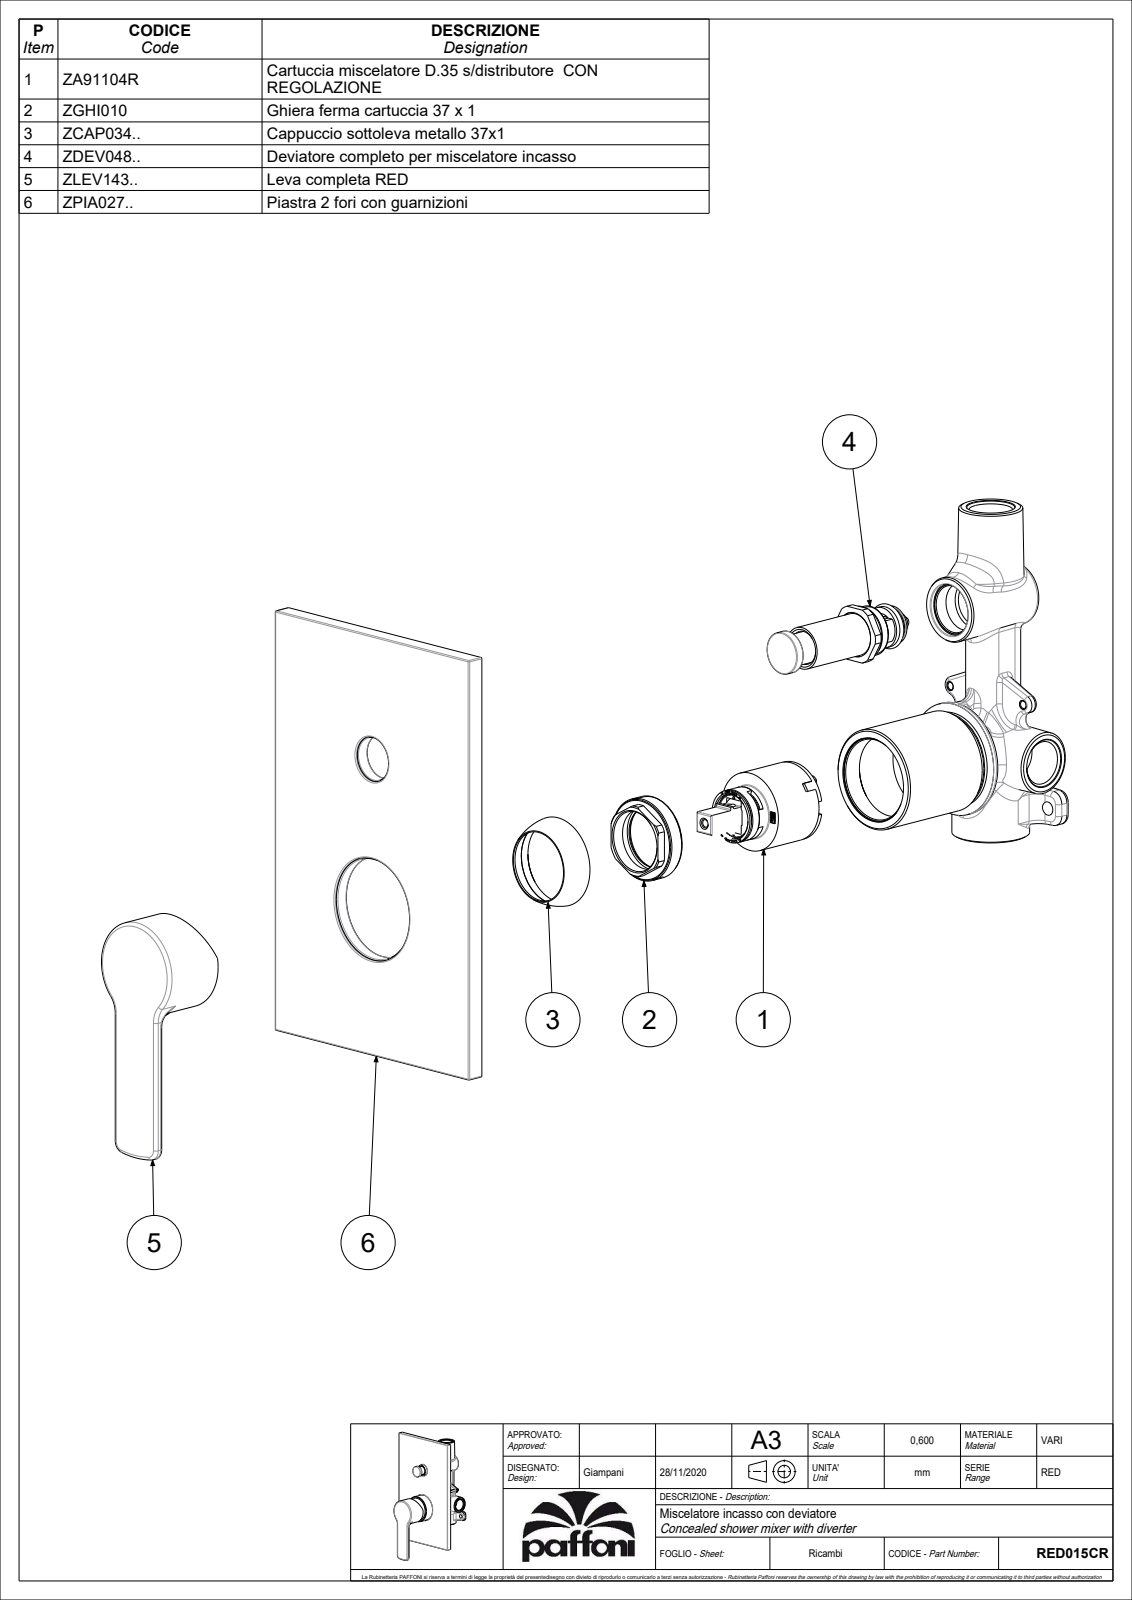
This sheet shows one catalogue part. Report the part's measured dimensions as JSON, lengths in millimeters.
{"part_name": "RED015CR", "step_written_by": "CREO PARAMETRIC BY PTC INC, 2020044 (CONFIG_CONTROL_DESIGN)", "units": "millimeters", "bodies": {"solids": 5, "faces": 1152, "planar": 617, "cylindrical": 301, "other": 234}, "overall_size": [209, 120, 64.83], "volume_mm3": 171443, "surface_area_mm2": 98513, "round_holes": [[3.3, 2], [4, 2], [3, 1], [4.5, 1], [5, 1], [10.5, 1], [14.8, 1], [19.2, 1], [19.5, 1], [19.9, 1], [20, 1], [23.2, 1]], "round_bosses_or_shafts": [[51, 1], [49, 1], [44.8, 1], [43, 1], [35, 1], [32.2, 1], [25, 1], [23.5, 1]], "partial_cylinders_radius": [[0.5, 74], [0.15, 11], [1, 10], [0.3, 4], [1.5, 4], [5, 2], [10, 2], [7, 1]], "face_to_face_distances": [7.5, 2.5, 5, 0.5, 5.5, 8, 22.5, 59.1, 4.5, 60.1], "hole_center_spacings": [12.5, 68]}
